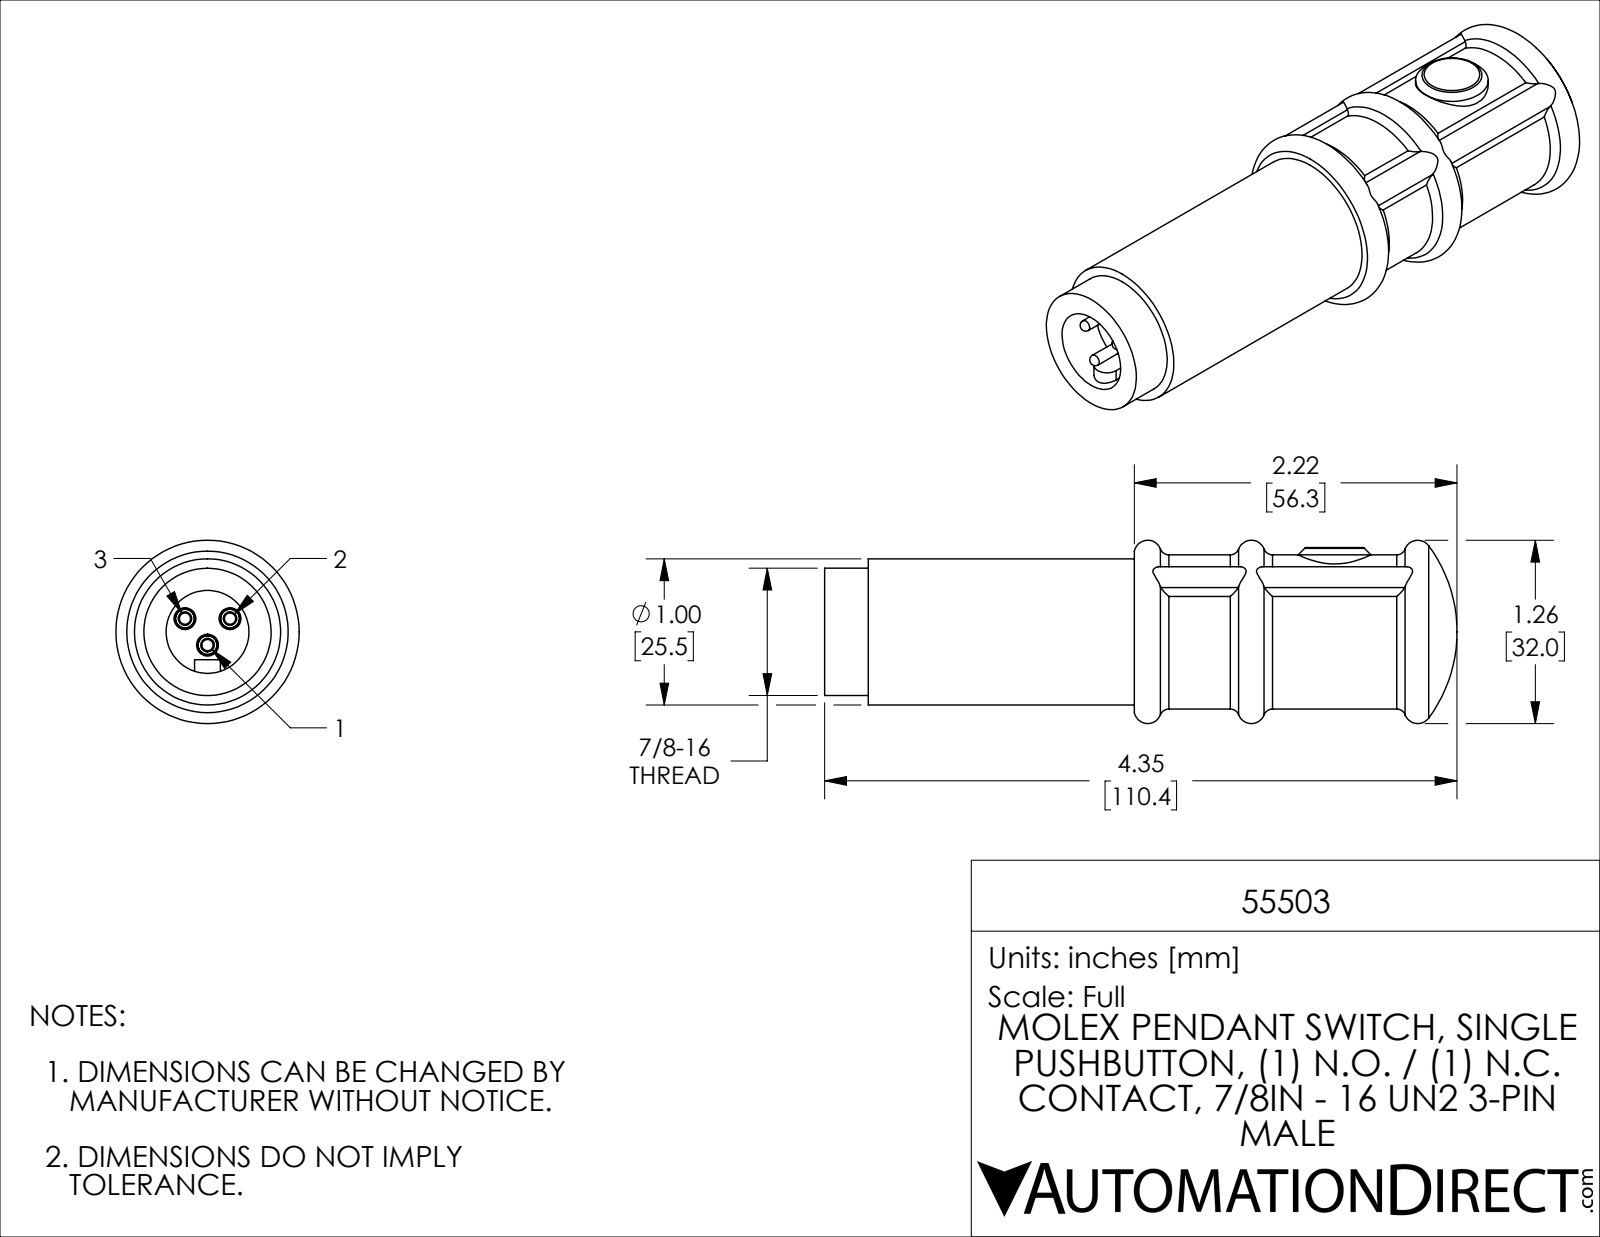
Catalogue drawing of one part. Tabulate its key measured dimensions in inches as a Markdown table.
| quantity | value |
| --- | --- |
| part name | 55503 |
| STEP written by | SolidWorks 2021 (CONFIG_CONTROL_DESIGN) |
| units | inches |
| bodies | 4 solids, 99 faces (14 planar, 40 cylindrical, 45 other) |
| overall size | 4.348 × 1.26 × 1.26 |
| volume | 3.661 in³ |
| surface area | 18.13 in² |
| round holes (diameter × count) | 0.57 × 1 |
| round bosses / shafts (diameter × count) | 0.077 × 3, 1.059 × 1, 1.005 × 1, 0.875 × 1, 0.5 × 1 |
| partial cylindrical surfaces (radius × count) | 0.062 × 4, 0.094 × 3, 0.089 × 1, 0.529 × 1 |
| main face-to-face distances | 0.333, 0.3, 0.033, 2.13, 1.83, 1.797, 0.771, 0.178, 0.243, 0.057 |
